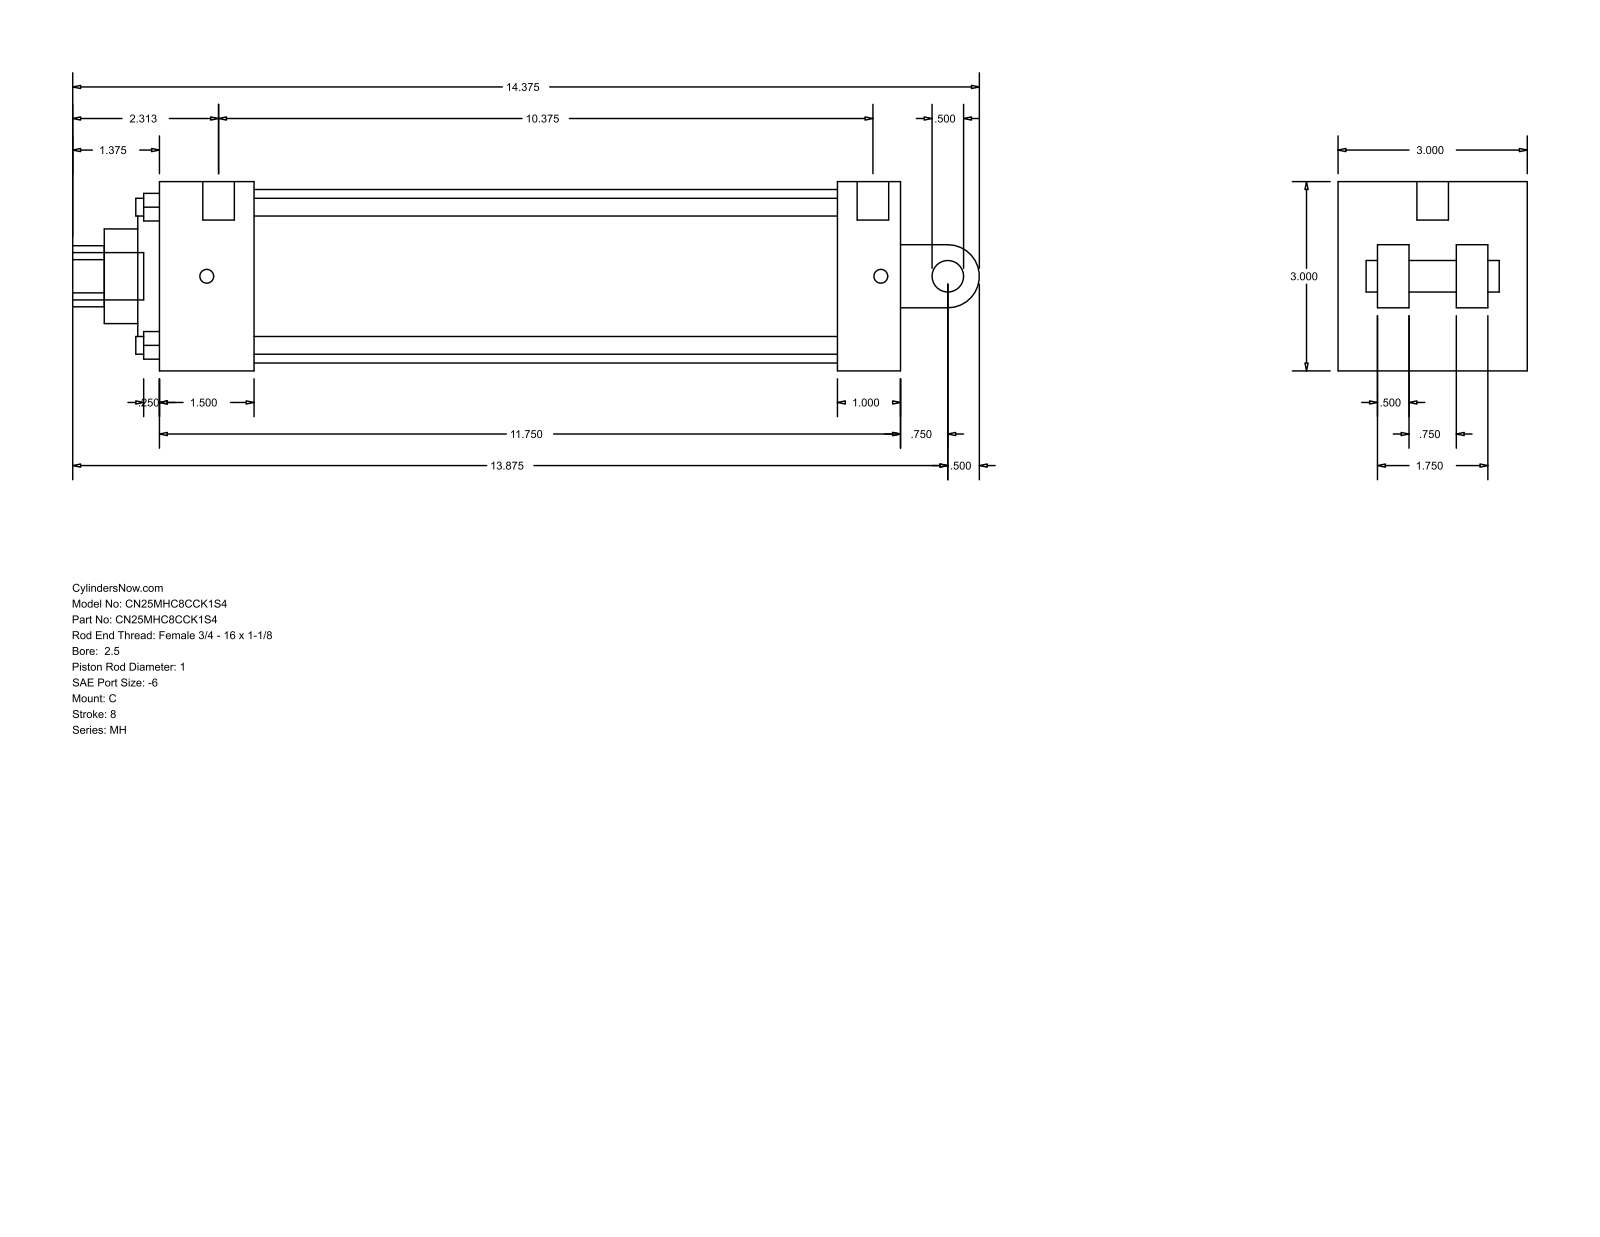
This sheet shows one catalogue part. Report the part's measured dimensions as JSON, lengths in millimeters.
{"part_name": "MH_C__0250_1", "step_written_by": "GSSL Pune (CONFIG_CONTROL_DESIGN)", "units": "millimeters", "bodies": {"solids": 0, "faces": 101, "planar": 71, "cylindrical": 30, "other": 0}, "overall_size": [365.12, 76.2, 76.2], "round_holes": [[7.14, 4], [5.56, 2], [12.7, 1], [25.4, 1], [38.1, 1], [60.33, 1], [69.85, 1]], "round_bosses_or_shafts": [[12.7, 2], [5.56, 2], [19.05, 1]], "partial_cylinders_radius": [[12.29, 1], [12.7, 1]], "face_to_face_distances": [76.2, 25.4, 298.46, 15.87, 60.33, 273.06, 38.11, 234.95, 260.35, 12.7], "hole_center_spacings": [39.33, 55.62, 78.66, 3.18]}
